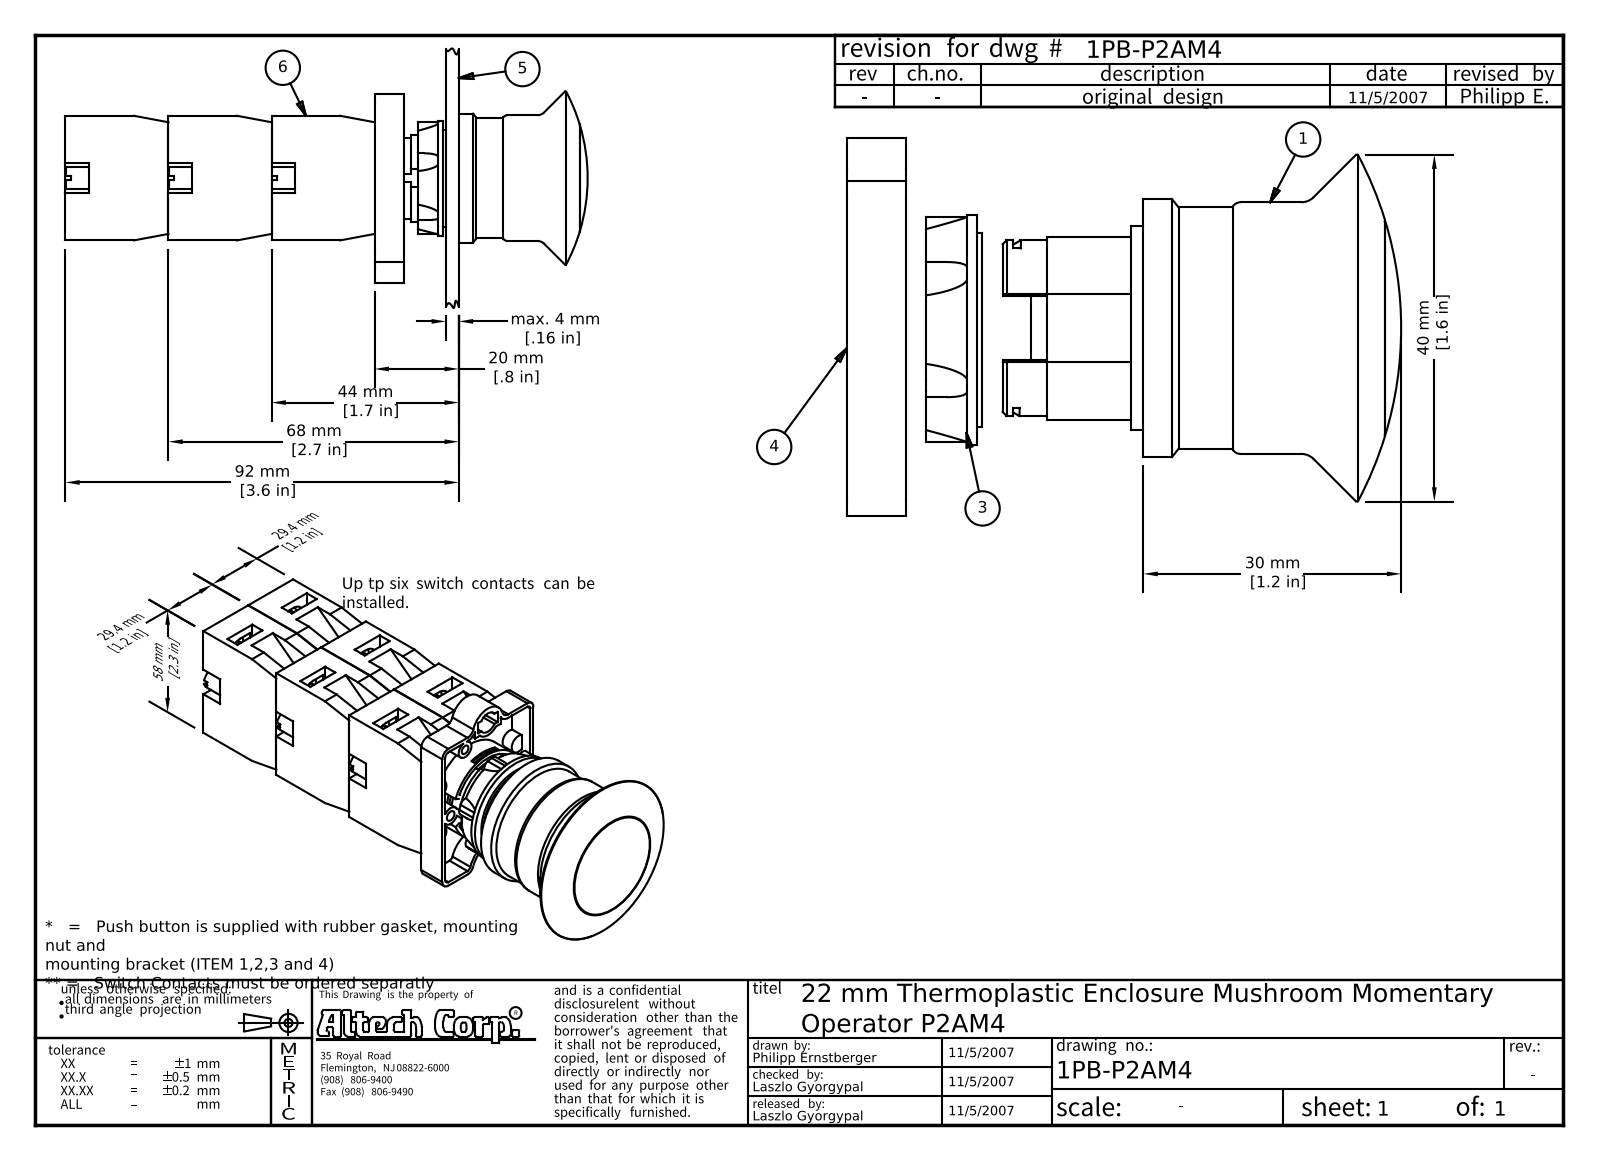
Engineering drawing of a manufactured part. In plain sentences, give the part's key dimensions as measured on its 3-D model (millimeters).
The part is named "P2AM4_assembly; P2AM4_operator; P2AM4; 2PRG1 (+7 more)". Its 3-D file was written by "Autodesk Inventor 2008 (AUTOMOTIVE_DESIGN)". It is 29 solids with 1162 faces: 627 planar, 197 cylindrical and 338 other. Overall it measures 121.6 by 60.45 by 45 millimeters. Its volume is 88 119 cubic millimeters and its surface area 46 844 square millimeters. Round holes: 6 of diameter 2.5, 2 of diameter 2.2, 2 of diameter 2.6, 1 of diameter 17.6, 1 of diameter 20.8, 1 of diameter 22.5, 1 of diameter 28.3. Round bosses or shafts: 6 of diameter 3, 4 of diameter 2.75, 4 of diameter 1.5, 2 of diameter 5, 2 of diameter 4.2, 1 of diameter 30, 1 of diameter 29.3, 1 of diameter 28.1. Partial cylindrical surfaces (rounded edges, fillets, slot ends): 15 of radius 1, 12 of radius 1.5, 8 of radius 2, 6 of radius 2.25, 2 of radius 3, 2 of radius 3.3, 2 of radius 5, 1 of radius 2.6. The main face-to-face distances are 14.8, 14.7, 24, 3, 48, 29.5, 19.6, 29, 16.6, 64.6. The hole center spacings are 6.54, 26.07, 11.41, 12.25, 13, 14.51, 14.56, 17.17.
